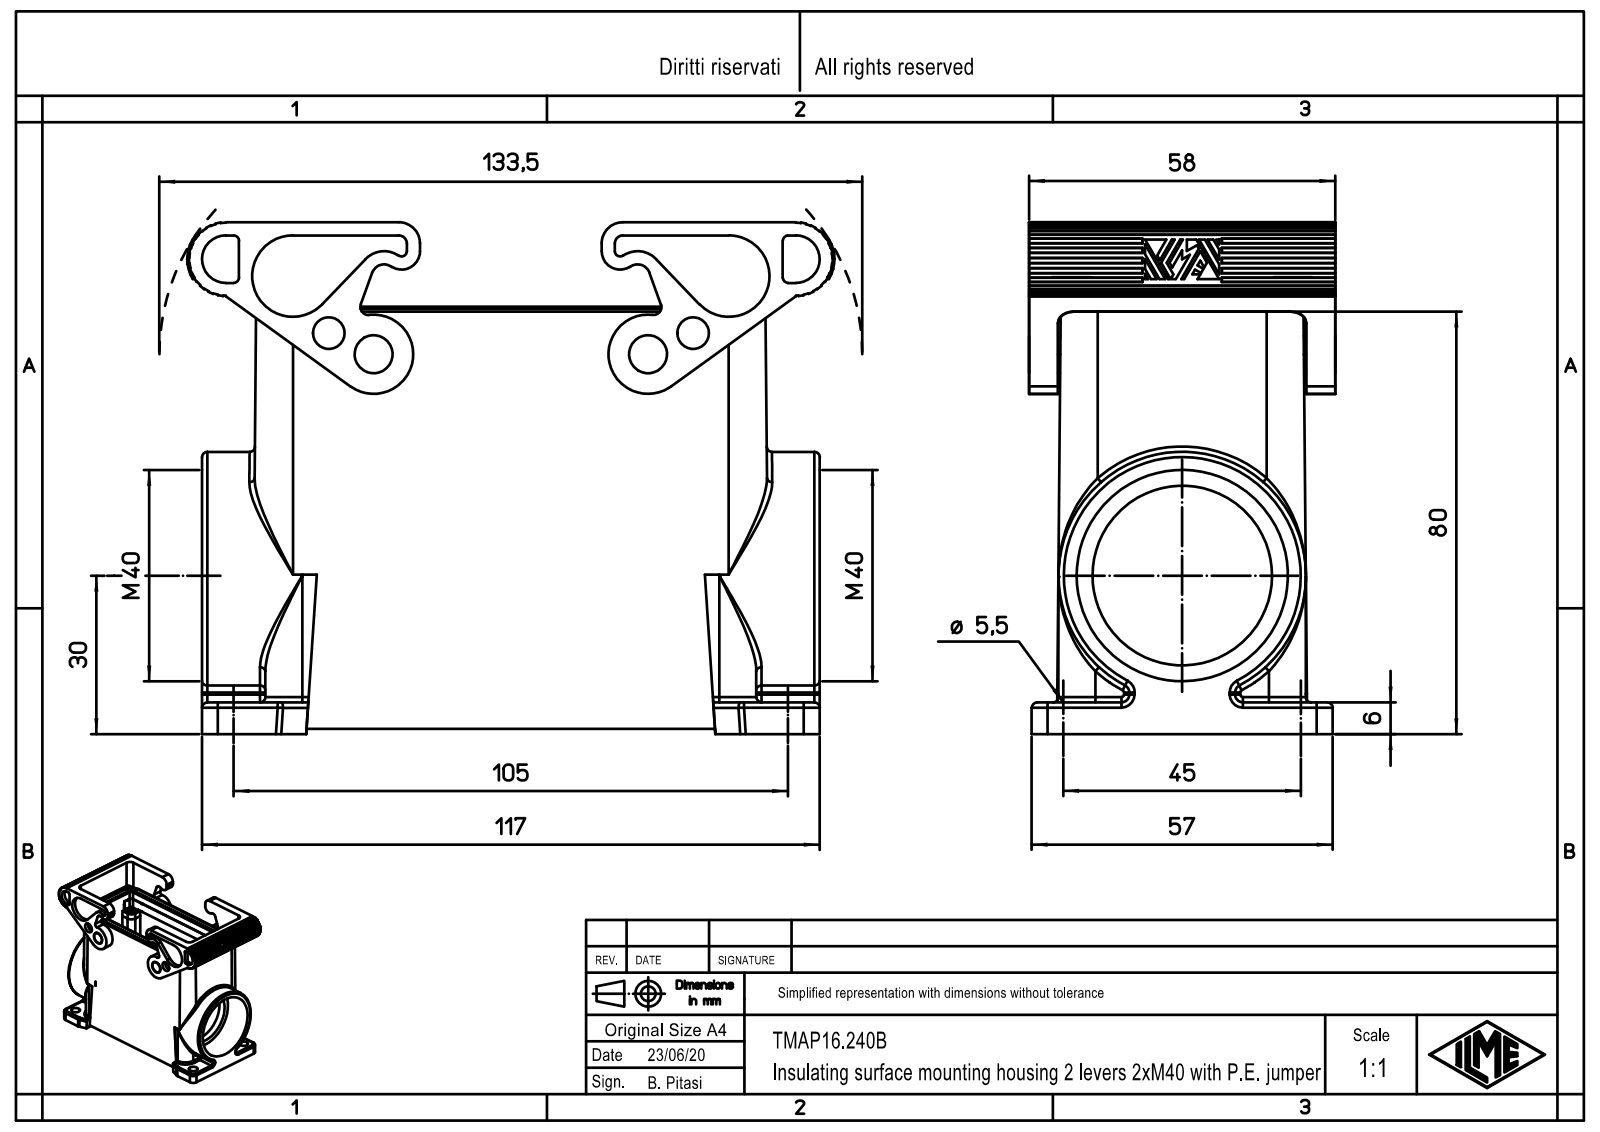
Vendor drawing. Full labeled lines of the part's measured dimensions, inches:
Part name (STEP PRODUCT): TMAP16.240B
STEP written by: Creo Elements/Direct Modeling 20.1B 02-Apr-2019 (C) Parametric Technology GmbH (AUTOMOTIVE_DESIGN)
Units: inches
Bodies: 1 solid, 939 faces (533 planar, 282 cylindrical, 124 other)
Overall size (bounding box): 4.827 × 3.815 × 2.283
Volume: 11.16 in³ · Surface area: 116.1 in²
Round holes (diameter × count): ⌀0.118 ×4, ⌀0.138 ×4, ⌀0.217 ×4, ⌀0.236 ×2, ⌀0.394 ×2, ⌀1.339 ×1, ⌀1.575 ×1
Round bosses / shafts (diameter × count): ⌀0.189 ×4, ⌀0.276 ×2, ⌀1.845 ×1
Partial cylindrical surfaces — rounded edges, fillets, slot ends (radius × count): R0.039 ×22, R0.059 ×20, R0.118 ×12, R0.138 ×6, R0.276 ×6, R0.02 ×4, R0.051 ×4, R0.063 ×4
Main face-to-face distances: 1.598, 0.217, 0.256, 0.039, 2.067, 0.098, 2.185, 1.969, 0.118, 0.02
Hole centre spacings: 0.647, 1.517, 3.61, 3.862, 0.37, 1.063, 1.772, 2.387
